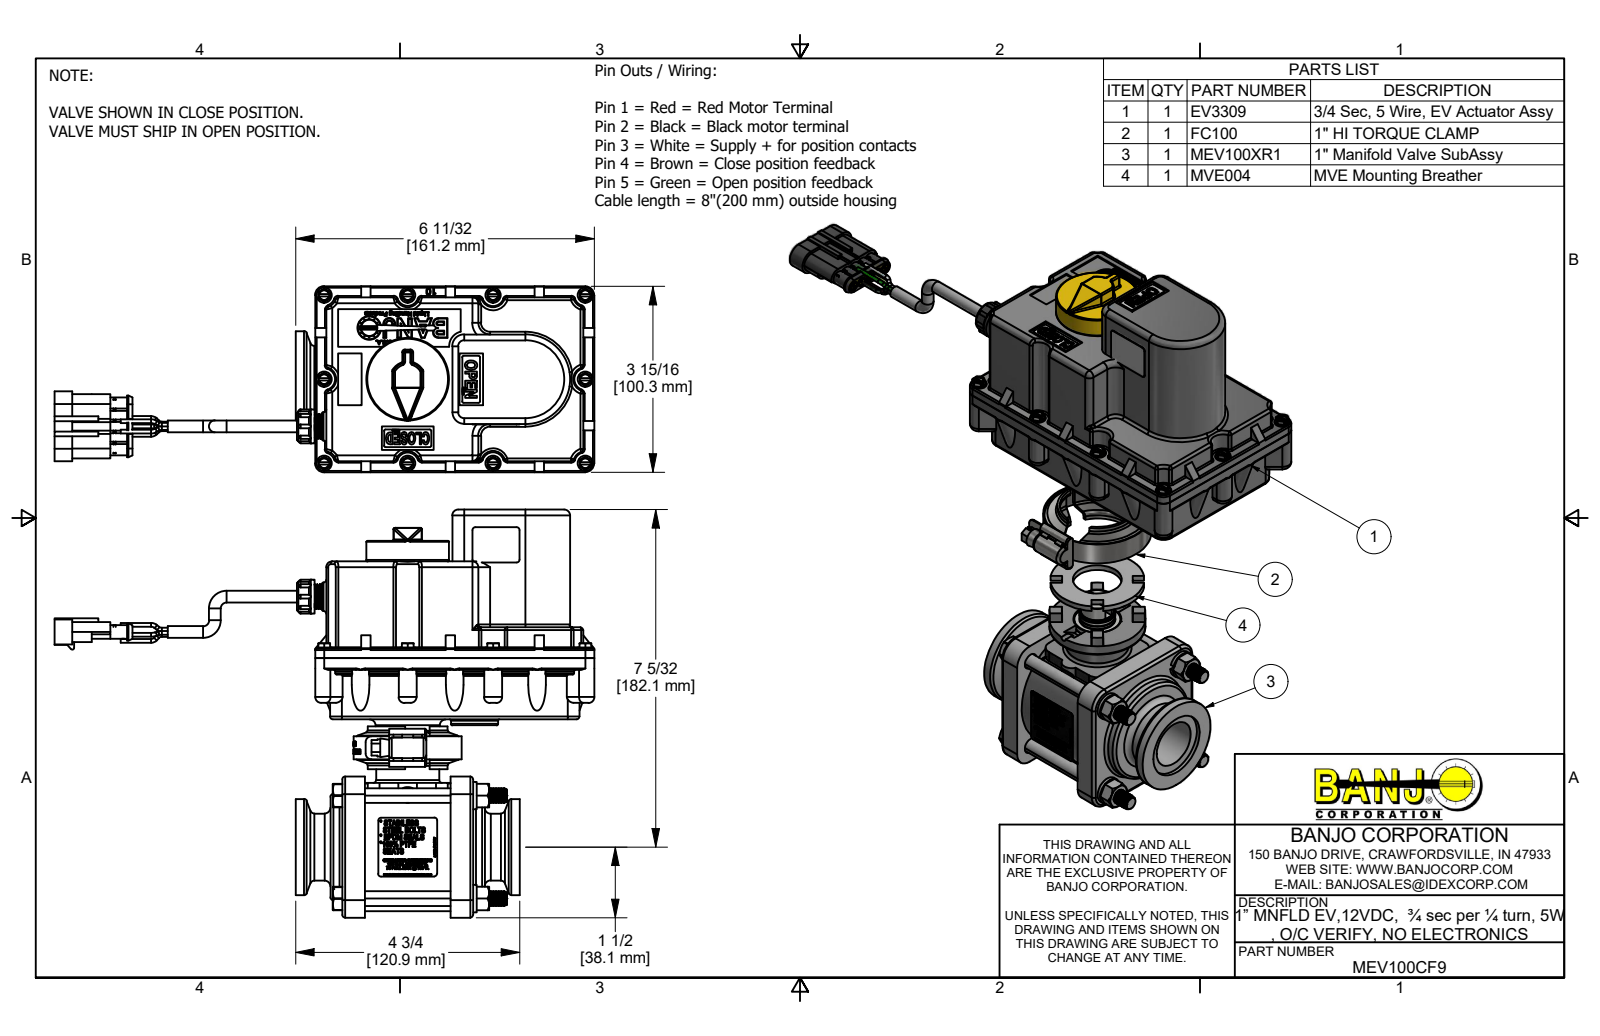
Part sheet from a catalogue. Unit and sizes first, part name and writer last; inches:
Units: inches
Overall size (bounding box): 11.465 × 8.668 × 3.95
Round holes (diameter × count): ⌀0.16 ×11, ⌀0.11 ×10, ⌀0.2 ×10, ⌀0.12 ×6, ⌀0.15 ×6, ⌀0.176 ×6, ⌀0.055 ×5, ⌀0.217 ×5, ⌀0.252 ×4, ⌀0.322 ×4, ⌀0.35 ×4, ⌀1.02 ×3
Round bosses / shafts (diameter × count): ⌀0.268 ×60, ⌀0.08 ×19, ⌀0.328 ×10, ⌀0.138 ×10, ⌀0.103 ×8, ⌀0.232 ×5, ⌀0.173 ×5, ⌀0.154 ×5
Partial cylindrical surfaces — rounded edges, fillets, slot ends (radius × count): R0.03 ×132, R0.06 ×67, R0.02 ×63, R0.125 ×28, R0.315 ×24, R0.5 ×24, R0.02 ×21, R0.062 ×21
Main face-to-face distances: 0.125, 0.125, 2.3, 0.2, 1.1, 0.78, 1.3, 3.23, 0.79, 2.565
Hole centre spacings: 1.68, 2.058, 1.684, 1.785, 2.376, 0.236, 0.492, 1.188
Volume: 55.32 in³ · Surface area: 608.3 in²
Bodies: 73 solids, 8462 faces (3697 planar, 1868 cylindrical, 2897 other)
Part name (STEP PRODUCT): MEV100CF9; MEV100XR1; MEV10254A; MEV10254AX (+8 more)
STEP written by: Autodesk Inventor 2019 (AUTOMOTIVE_DESIGN)
